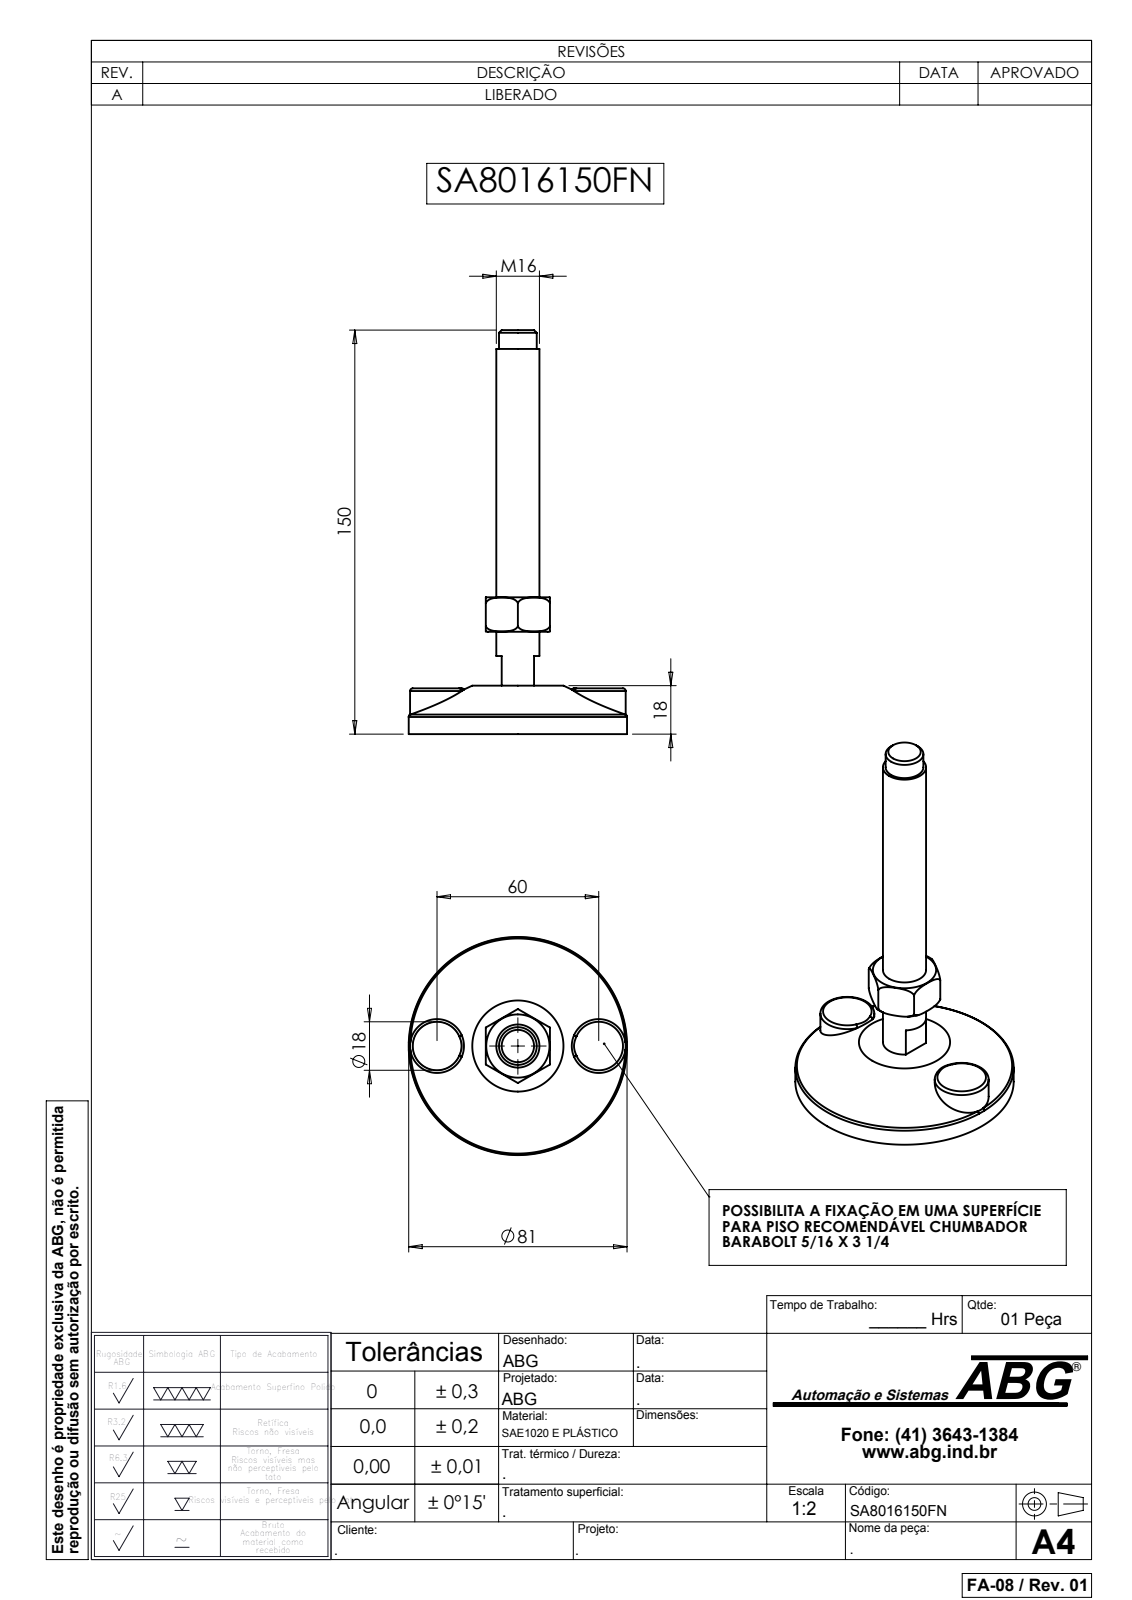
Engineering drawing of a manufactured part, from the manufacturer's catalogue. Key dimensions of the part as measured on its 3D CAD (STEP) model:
Part name (STEP PRODUCT): SA8016150FN
STEP written by: SolidWorks 2007 (CONFIG_CONTROL_DESIGN)
Units: millimetres
Bodies: 1 solid, 53 faces (18 planar, 14 cylindrical, 21 other)
Overall size (bounding box): 150 × 81 × 81
Volume: 98 970 mm³ · Surface area: 20 592 mm²
Round bosses / shafts (diameter × count): ⌀20 ×2, ⌀81 ×1, ⌀16 ×1, ⌀14 ×1
Main face-to-face distances: 18, 17, 1, 23.8, 5.9, 17.9, 50.8, 33.8, 32.8, 38
